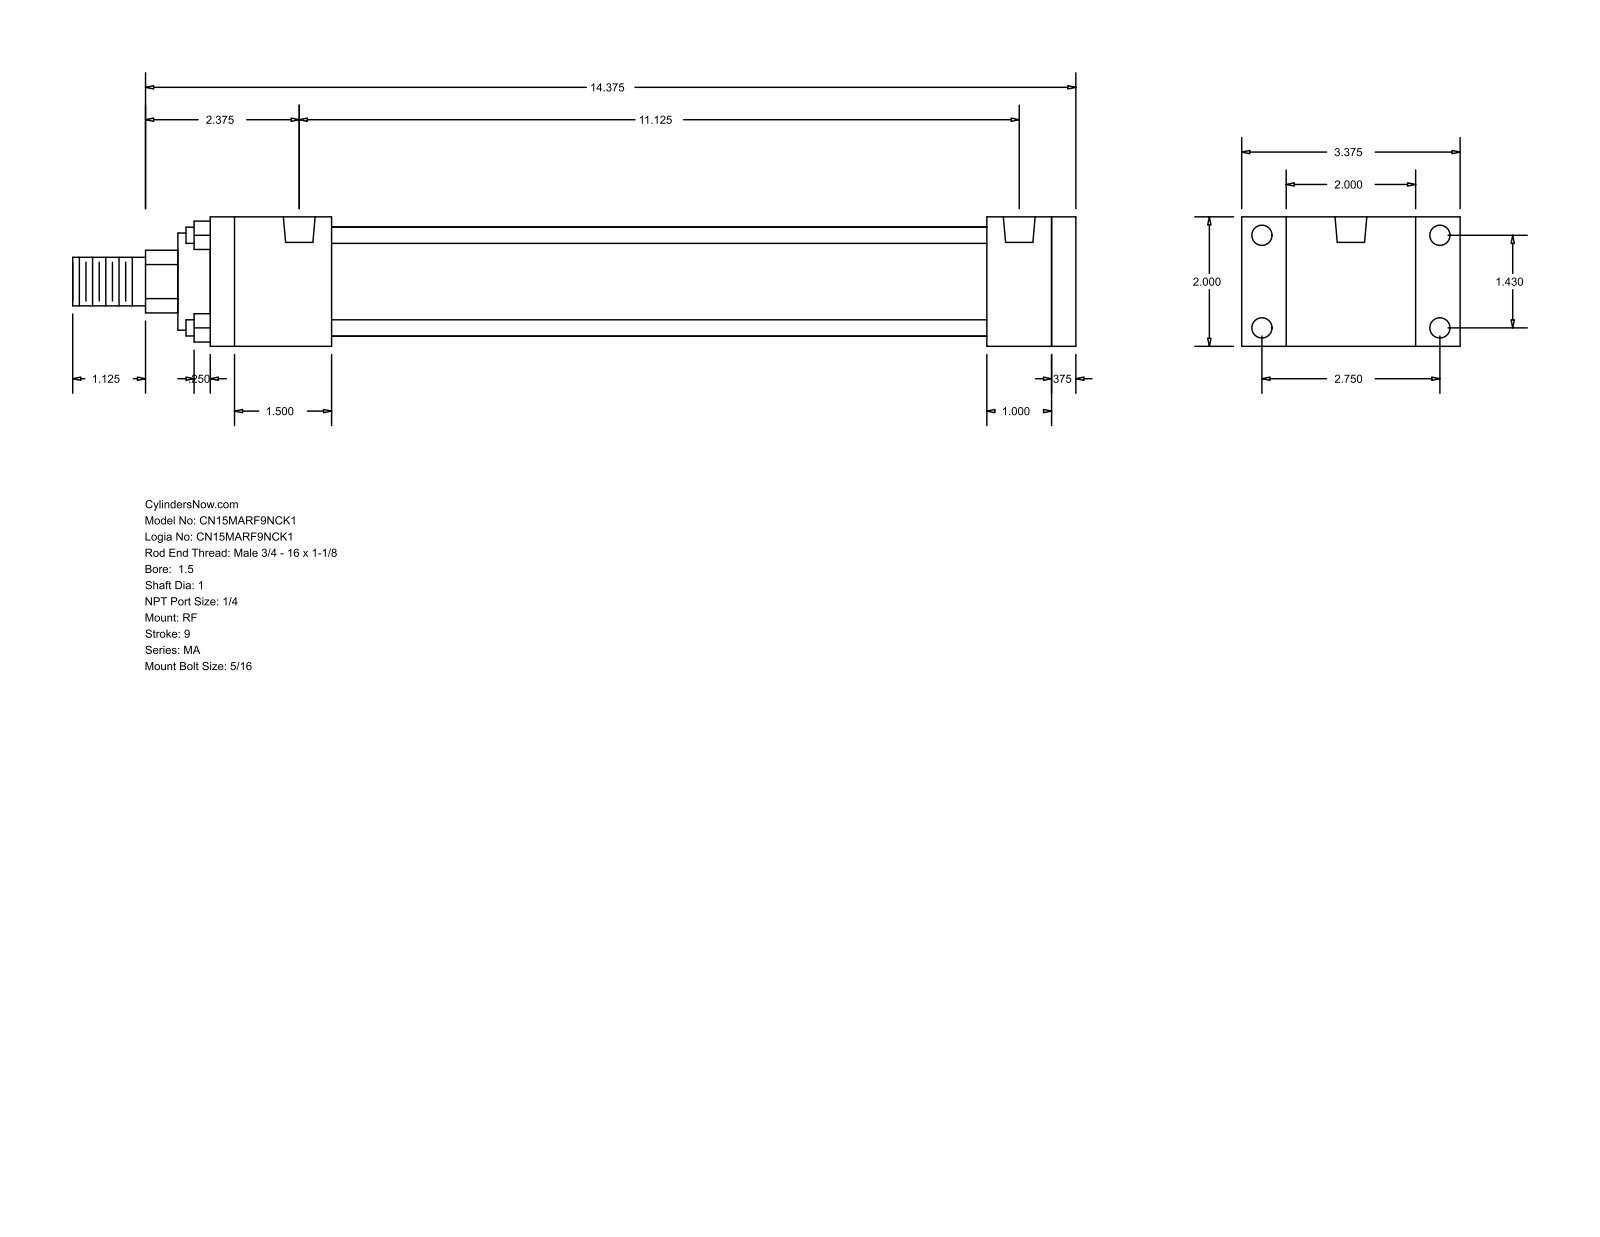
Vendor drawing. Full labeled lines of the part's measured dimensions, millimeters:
Part name (STEP PRODUCT): MA_RF__0150_1
STEP written by: GSSL Pune (CONFIG_CONTROL_DESIGN)
Units: millimetres
Bodies: 0 solids, 92 faces (64 planar, 28 cylindrical, 0 other)
Overall size (bounding box): 393.7 × 85.72 × 50.8
Round holes (diameter × count): ⌀7.94 ×8, ⌀12.49 ×2
Round bosses / shafts (diameter × count): ⌀6.35 ×4, ⌀42.93 ×1, ⌀38.1 ×1, ⌀25.4 ×1, ⌀19.05 ×1
Partial cylindrical surfaces — rounded edges, fillets, slot ends (radius × count): R12.29 ×1
Main face-to-face distances: 50.8, 9.52, 339.72, 330.2, 25.4, 304.8, 34.92, 47.63, 257.17, 282.57
Hole centre spacings: 36.32, 69.84, 78.72, 282.57
